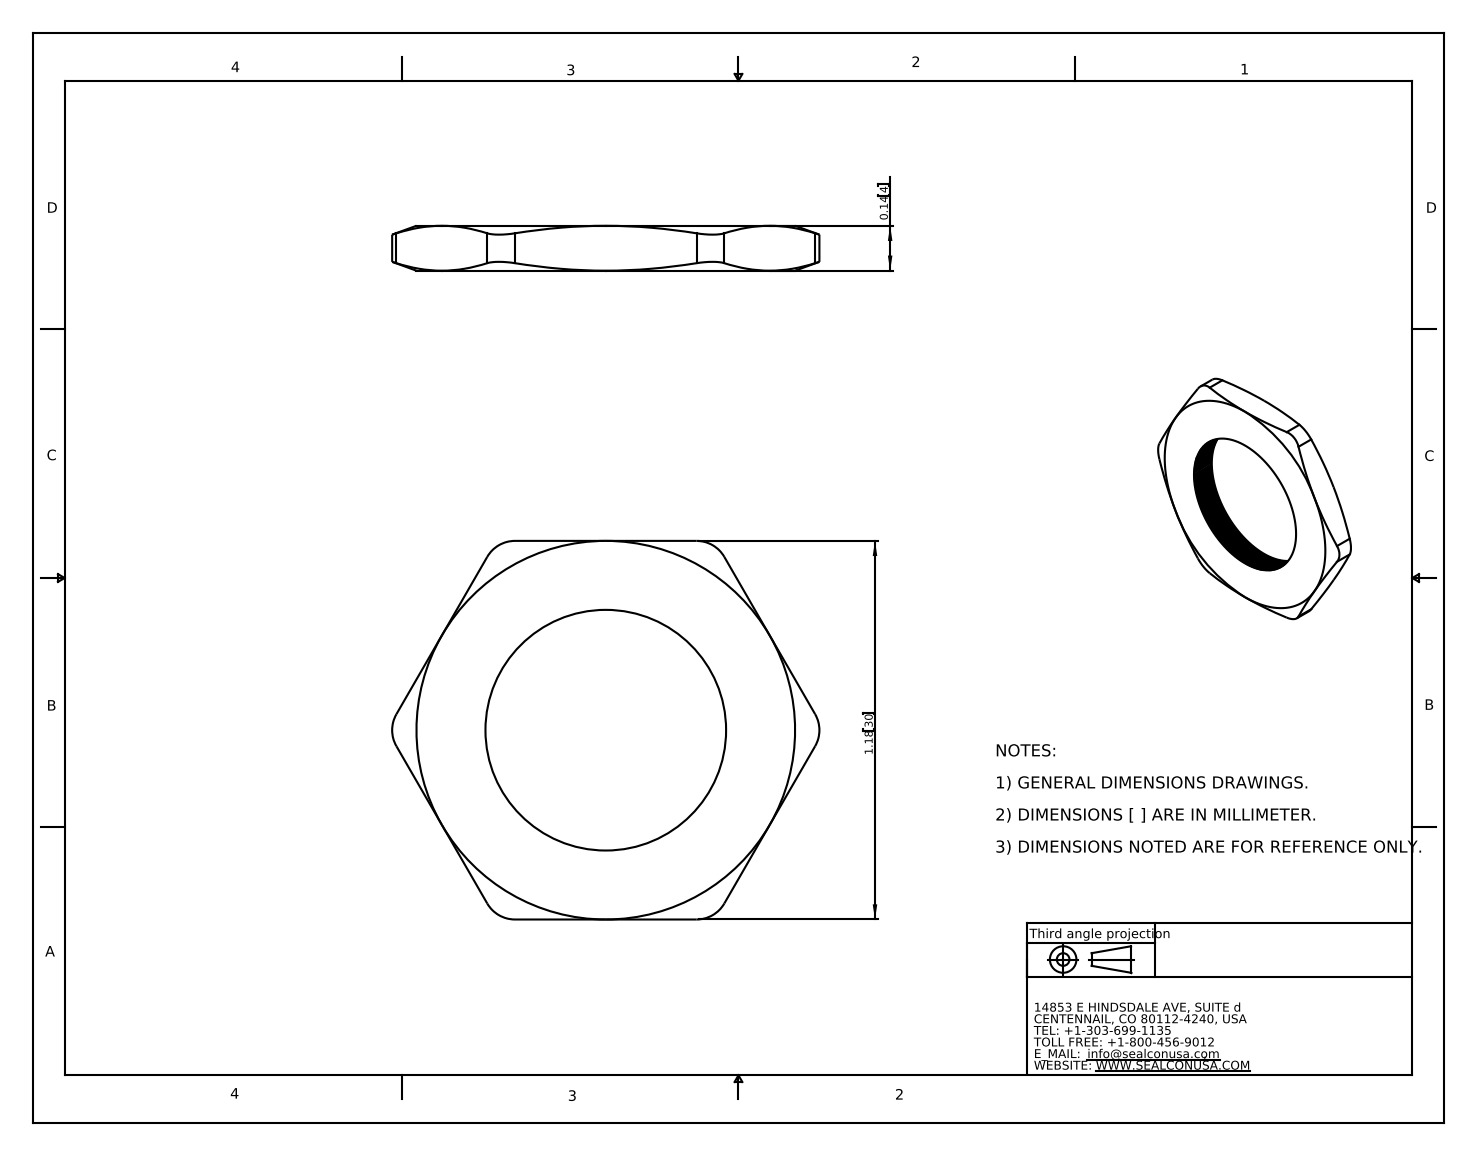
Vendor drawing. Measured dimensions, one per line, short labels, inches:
name: NN-21-BR
written by: SolidWorks 2008 (CONFIG_CONTROL_DESIGN)
unit: in
bodies: 1 solid, 97 faces (8 planar, 7 cylindrical, 82 other)
size: 1.332 × 1.18 × 0.14
volume: 0.101 in³; area: 2.67 in²
rounds: 6× R0.1
face distances: 0.14, 1.18
